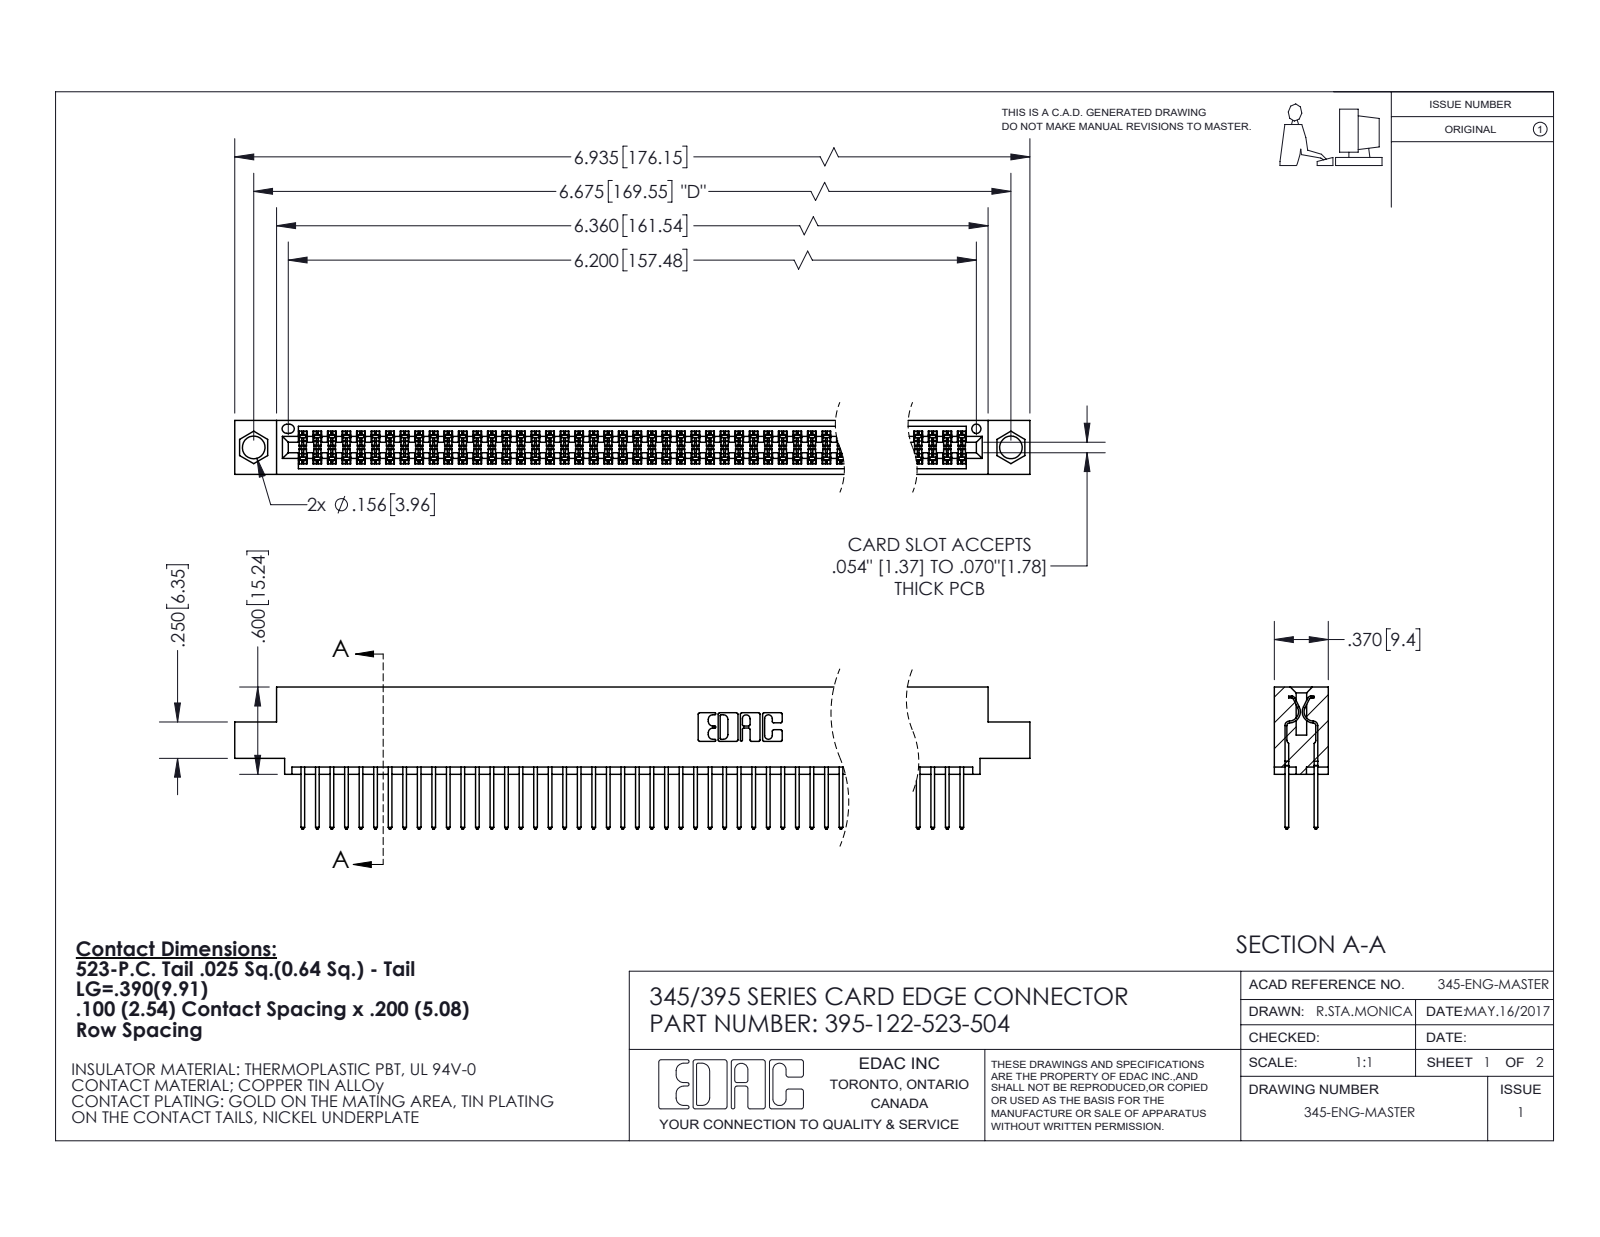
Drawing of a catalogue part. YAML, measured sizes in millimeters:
part_name: "345-292-001_345-293-123; 345 Part_0.110 Offset - 0.156 Dia-TI; 395-122-523-504"
step_written_by: "SolidWorks 2020 (CONFIG_CONTROL_DESIGN)"
units: millimeters
bodies: {solids: 123, faces: 6244, planar: 4124, cylindrical: 2120, other: 0}
overall_size: [176.1, 24.8, 9.4]
volume: 17350
surface_area: 27090
round_holes:
  - {diameter: 4, count: 2}
  - {diameter: 1.6, count: 1}
partial_cylinders:
  - {radius: 0.2, count: 183}
  - {radius: 0.3, count: 122}
  - {radius: 0.3, count: 22}
  - {radius: 0.2, count: 6}
  - {radius: 0.8, count: 6}
  - {radius: 0.7, count: 3}
  - {radius: 0.4, count: 2}
  - {radius: 0.5, count: 2}
face_to_face_distances: [1.8, 7.6, 5.1, 2.5, 6.9, 0.6, 9.4, 5.7, 4.4, 3.8]
hole_center_spacings: [6.9, 163.6, 169.5]
